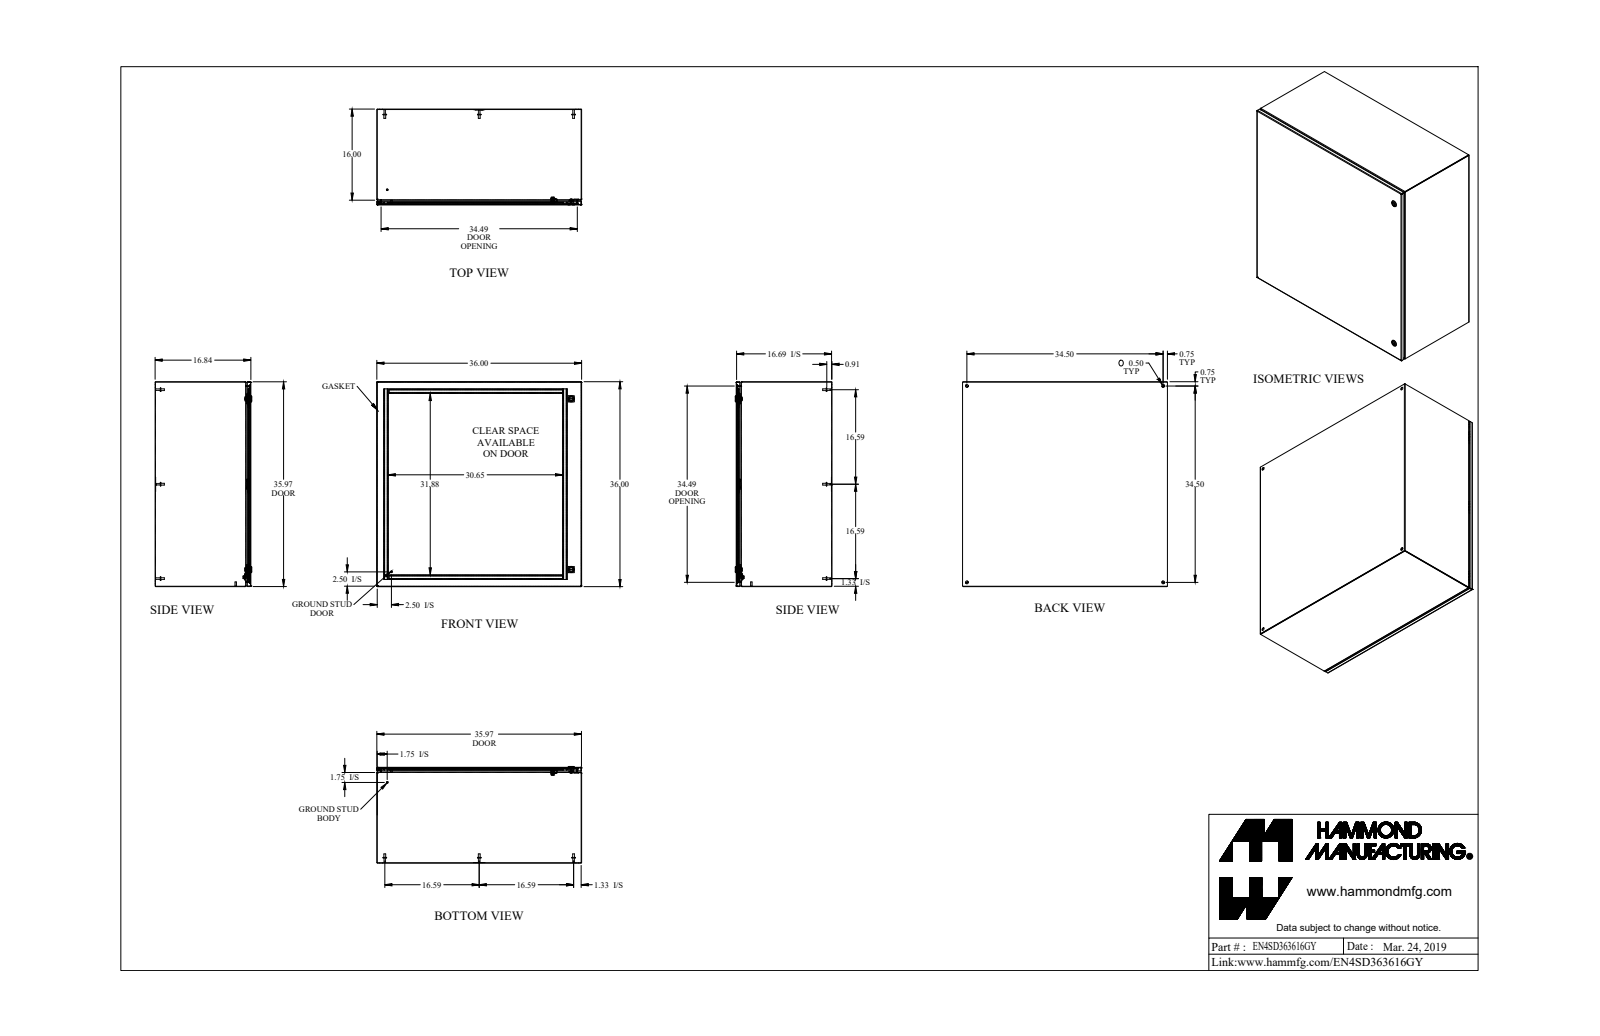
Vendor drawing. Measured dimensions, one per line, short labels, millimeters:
name: EN4SD363616GY
written by: SolidWorks 2019 (AUTOMOTIVE_DESIGN)
unit: mm
bodies: 43 solids, 1177 faces (559 planar, 395 cylindrical, 223 other)
size: 914.4 × 914.4 × 431.7
volume: 6 493 000 mm³; area: 7 212 000 mm²
holes: 4× ⌀12.7, 2× ⌀5.9, 2× ⌀15.9, 2× ⌀19.9, 1× ⌀4.4, 1× ⌀5, 1× ⌀6.1, 1× ⌀6.1, 1× ⌀7, 1× ⌀9.5
bosses: 8× ⌀8, 8× ⌀6.9, 6× ⌀15.9, 3× ⌀15.9, 2× ⌀27.9, 2× ⌀13.3, 2× ⌀7.1, 2× ⌀6.4
rounds: 24× R1.1, 24× R2.1, 18× R0.9, 18× R2.7, 12× R7.9, 10× R1.6, 10× R2.4, 9× R0.4
face distances: 1.8, 425.8, 912.6, 424, 427.7, 910.7, 914.4, 21.3, 404.6, 1
hole spacings: 876.3, 851, 1239.3, 63.3, 63.3, 90, 112.8, 762
